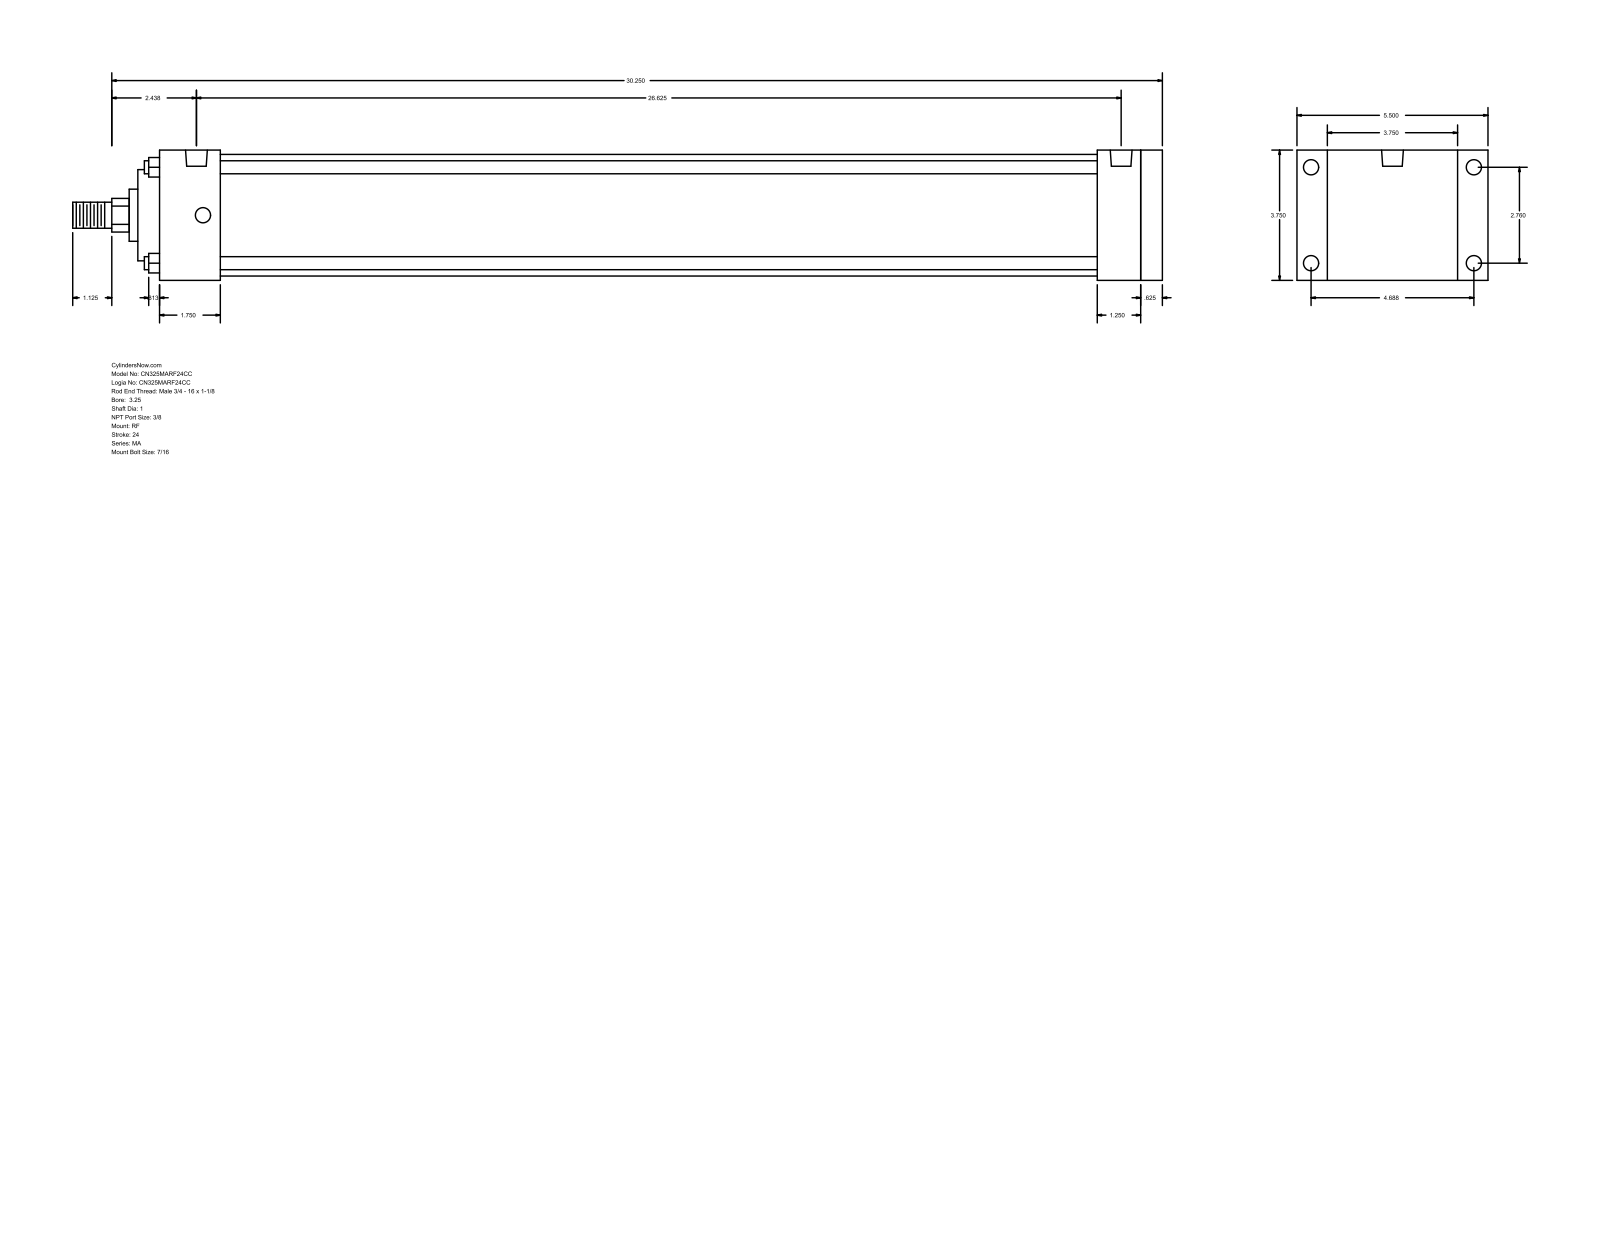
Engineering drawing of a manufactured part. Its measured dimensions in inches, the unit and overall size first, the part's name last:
Units: inches
Overall size (bounding box): 31.375 × 5.5 × 3.75
Round holes (diameter × count): ⌀0.437 ×8, ⌀0.627 ×2
Round bosses / shafts (diameter × count): ⌀0.375 ×4, ⌀3.5 ×1, ⌀2.625 ×1, ⌀1.5 ×1, ⌀1 ×1, ⌀0.75 ×1
Partial cylindrical surfaces — rounded edges, fillets, slot ends (radius × count): R0.484 ×1
Main face-to-face distances: 3.75, 28.875, 0.625, 28.25, 0.875, 4.625, 1.875, 29.5, 27, 1.25
Hole centre spacings: 2.76, 4.687, 5.439, 26.25, 0.187, 0.188, 26.437, 26.438
Bodies: 0 solids, 94 faces (65 planar, 29 cylindrical, 0 other)
Part name (STEP PRODUCT): MA_RF__0325_1
STEP written by: GSSL Pune (CONFIG_CONTROL_DESIGN)
